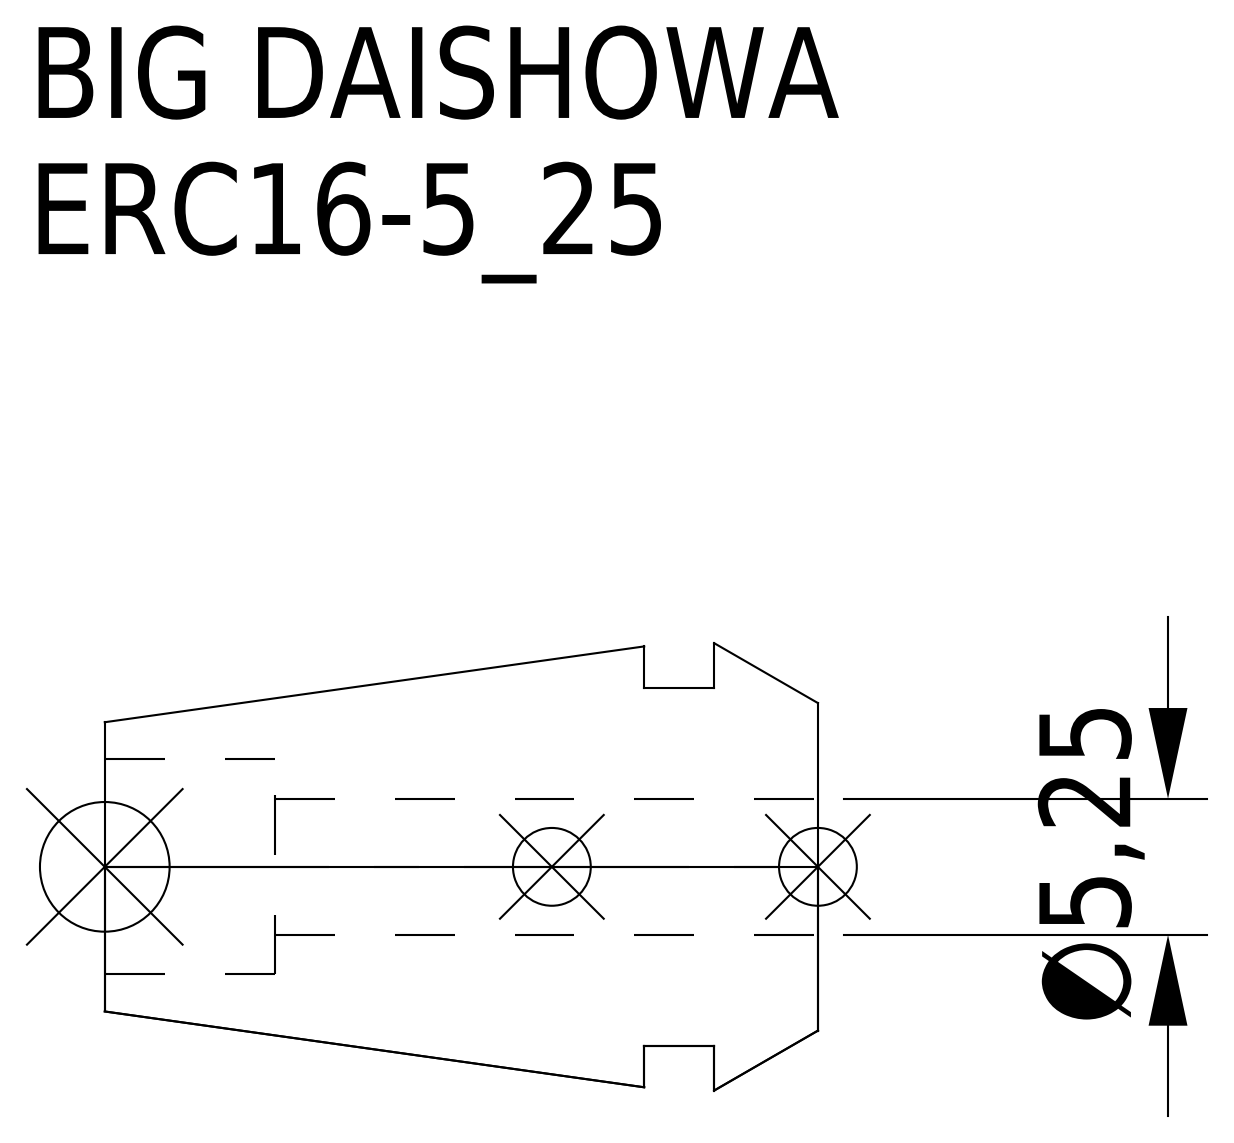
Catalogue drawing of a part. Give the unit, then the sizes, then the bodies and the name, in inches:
Units: inches
Overall size (bounding box): 1.083 × 0.679 × 0.679
Round holes (diameter × count): ⌀0.207 ×1, ⌀0.327 ×1
Round bosses / shafts (diameter × count): ⌀0.543 ×1
Main face-to-face distances: 0.157, 0.264, 0.106, 1.083, 0.925, 0.819, 0.824, 0.667, 0.561, 0.258
Volume: 0.219 in³ · Surface area: 3.288 in²
Bodies: 1 solid, 15 faces (5 planar, 6 cylindrical, 4 other)
Part name (STEP PRODUCT): ERC16-5_25
STEP written by: CREO PARAMETRIC BY PTC INC, 2016380 (AUTOMOTIVE_DESIGN)
